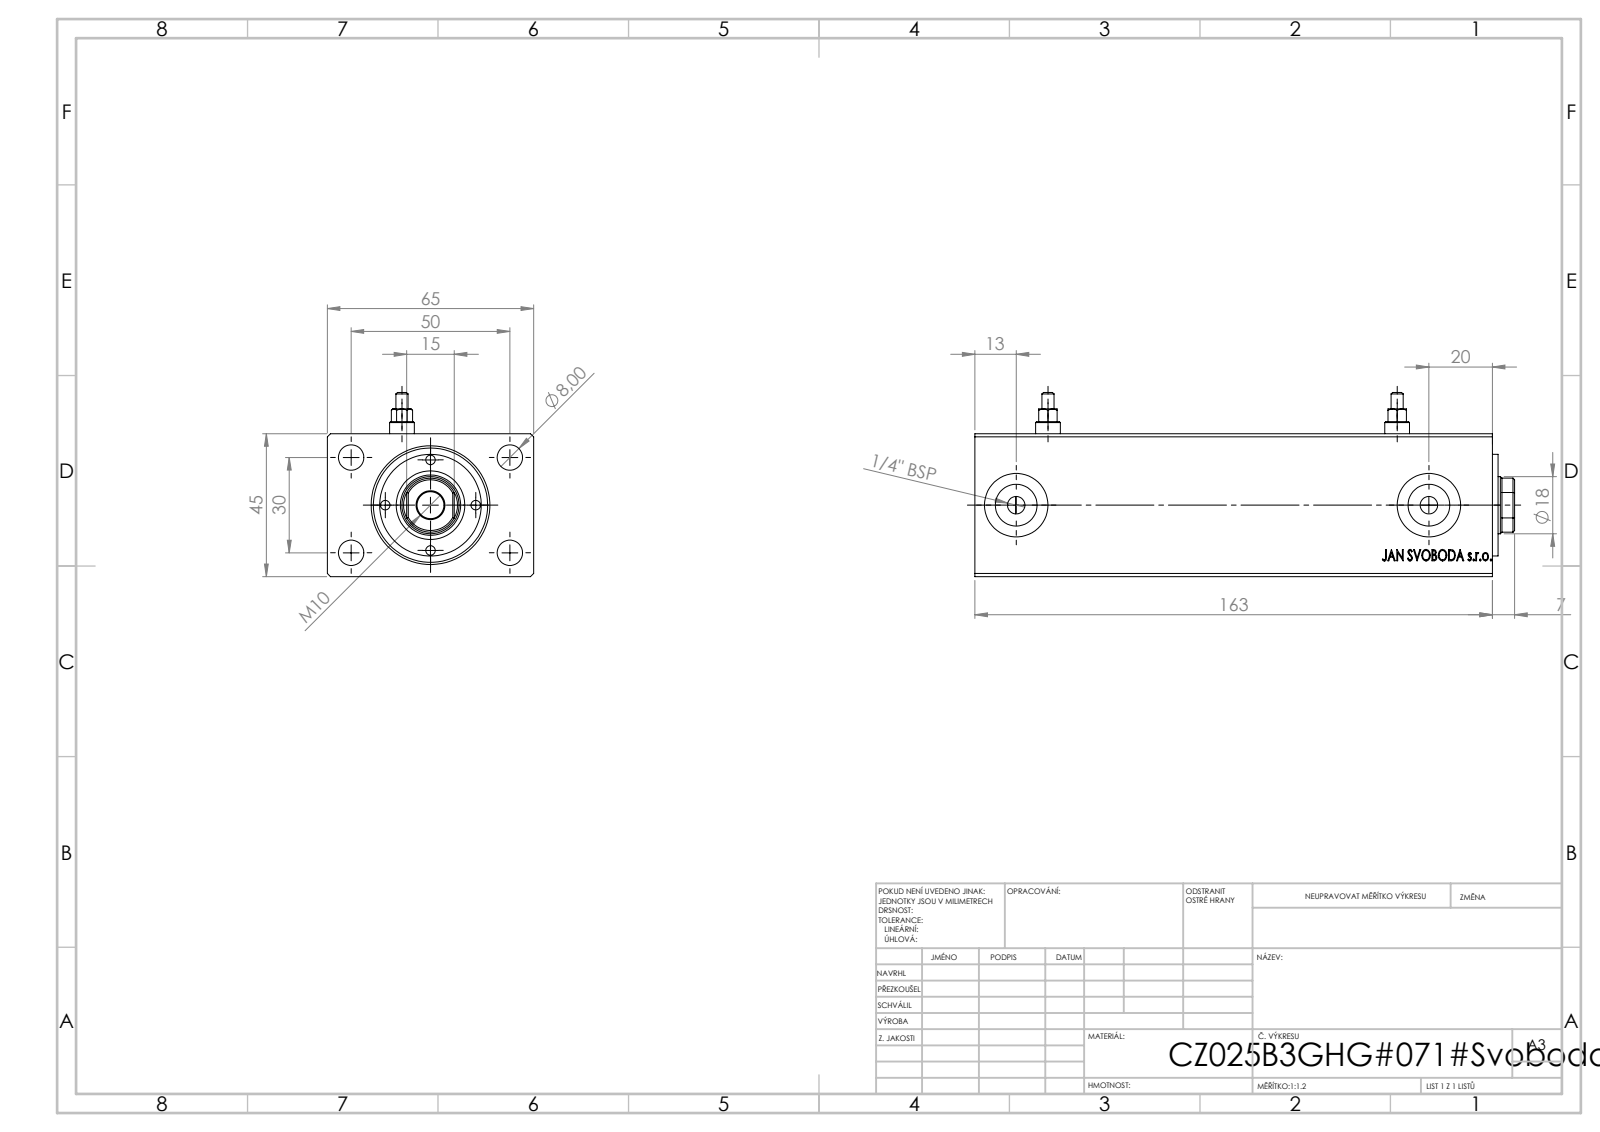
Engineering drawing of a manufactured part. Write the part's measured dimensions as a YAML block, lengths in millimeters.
part_name: "Zatka_Cushioning3; V500CZ; V500CZ_B_VC"
step_written_by: "SolidWorks 2019 (CONFIG_CONTROL_DESIGN)"
units: millimeters
bodies: {solids: 5, faces: 933, planar: 423, cylindrical: 74, other: 436}
overall_size: [170, 65, 58]
volume: 446066
surface_area: 75038
round_holes:
  - {diameter: 8, count: 6}
  - {diameter: 3, count: 4}
  - {diameter: 1.8, count: 2}
  - {diameter: 5.5, count: 2}
  - {diameter: 13.16, count: 2}
  - {diameter: 20, count: 2}
  - {diameter: 8.5, count: 1}
  - {diameter: 18, count: 1}
  - {diameter: 19, count: 1}
  - {diameter: 25, count: 1}
  - {diameter: 36, count: 1}
round_bosses_or_shafts:
  - {diameter: 7.8, count: 2}
  - {diameter: 3.8, count: 2}
  - {diameter: 32, count: 1}
partial_cylinders:
  - {radius: 8.5, count: 1}
face_to_face_distances: [45, 65, 163, 7, 162.8, 12.8, 150.2, 12.6, 1.8, 5.2]
hole_center_spacings: [14.25, 18.45, 20.15, 25.01, 29.15, 38.48, 42.02, 28.5]
